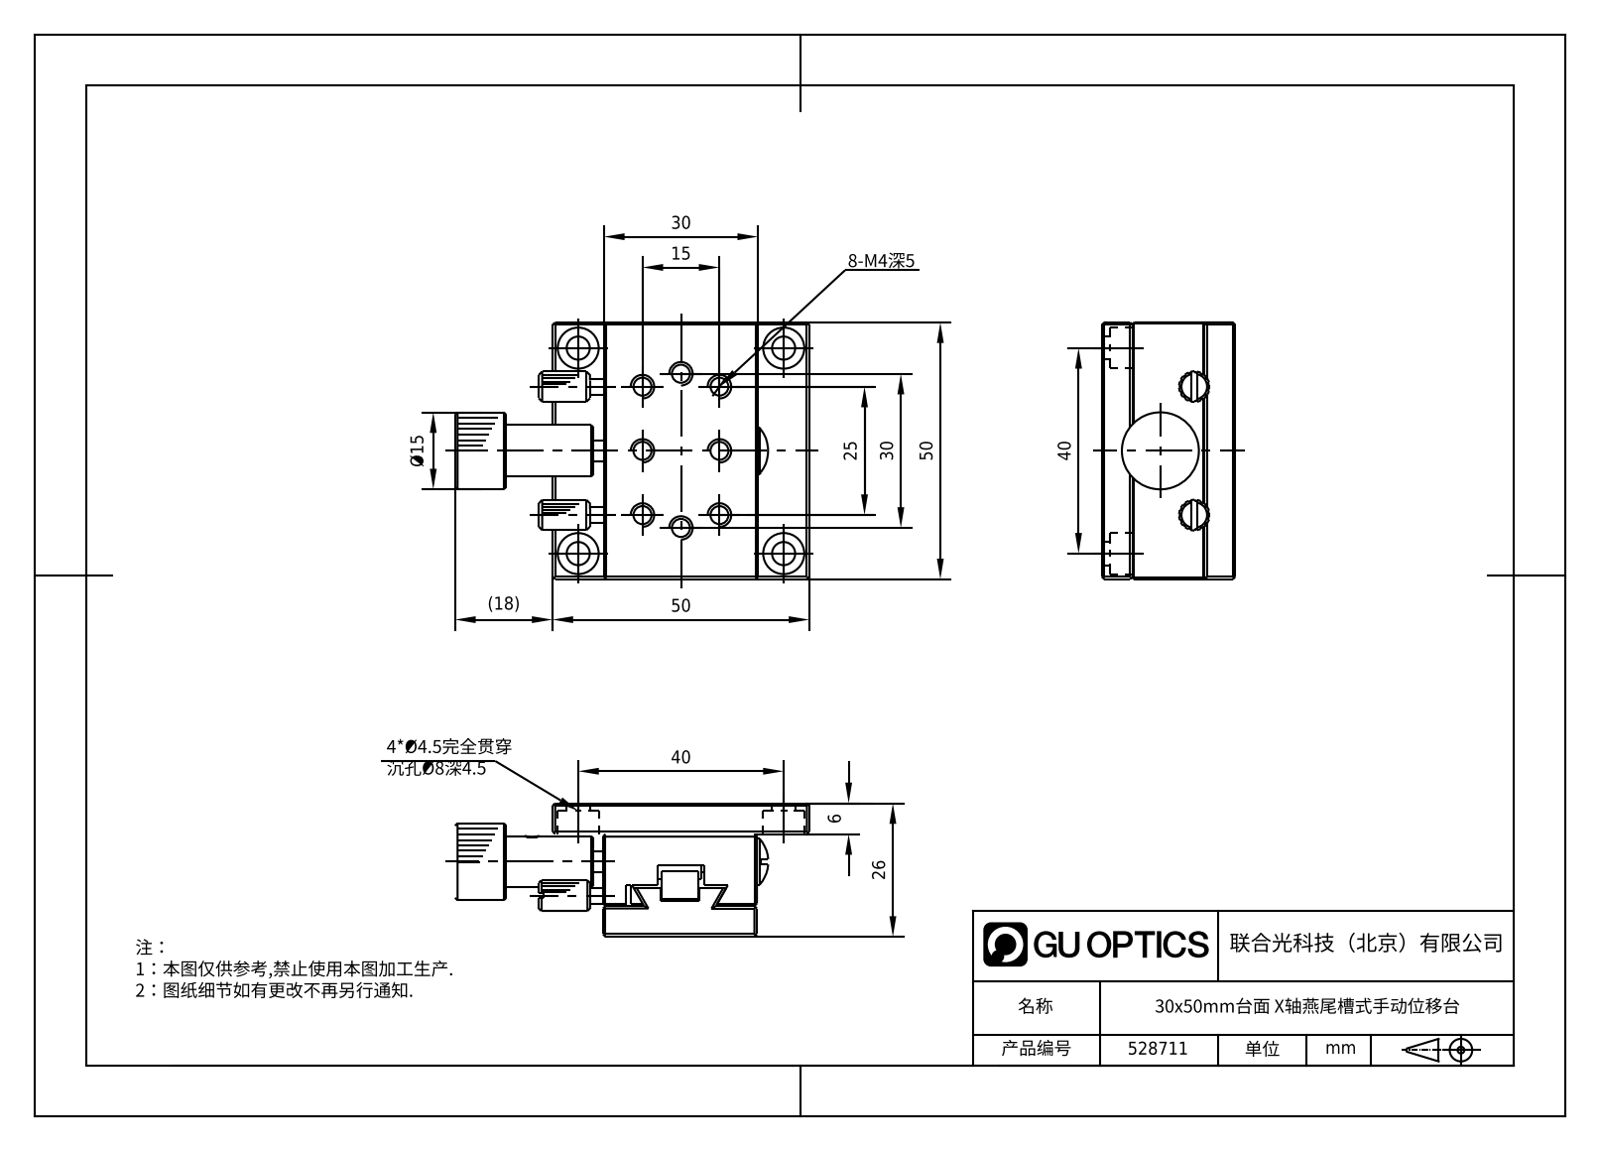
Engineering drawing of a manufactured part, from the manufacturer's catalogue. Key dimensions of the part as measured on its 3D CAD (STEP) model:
Part name (STEP PRODUCT): 528711
STEP written by: SolidWorks 2020 (CONFIG_CONTROL_DESIGN)
Units: millimetres
Bodies: 11 solids, 653 faces (391 planar, 132 cylindrical, 130 other)
Overall size (bounding box): 67 × 50 × 26
Volume: 43 215 mm³ · Surface area: 25 164 mm²
Round holes (diameter × count): ⌀4.5 ×11, ⌀8 ×9, ⌀3.3 ×8, ⌀2.5 ×7, ⌀1.6 ×2, ⌀2.05 ×2, ⌀2.4 ×2, ⌀7.7 ×2, ⌀4 ×1, ⌀4.1 ×1
Round bosses / shafts (diameter × count): ⌀9 ×4, ⌀7 ×2, ⌀2.95 ×2, ⌀2.6 ×2, ⌀8 ×1, ⌀7.5 ×1, ⌀6.85 ×1
Partial cylindrical surfaces — rounded edges, fillets, slot ends (radius × count): R7.5 ×1
Main face-to-face distances: 6, 20, 0.5, 19.5, 14, 5.5, 25.5, 50, 15.7, 26
Hole centre spacings: 23.58, 28.5, 34, 40, 15, 7.91, 8, 9.01
